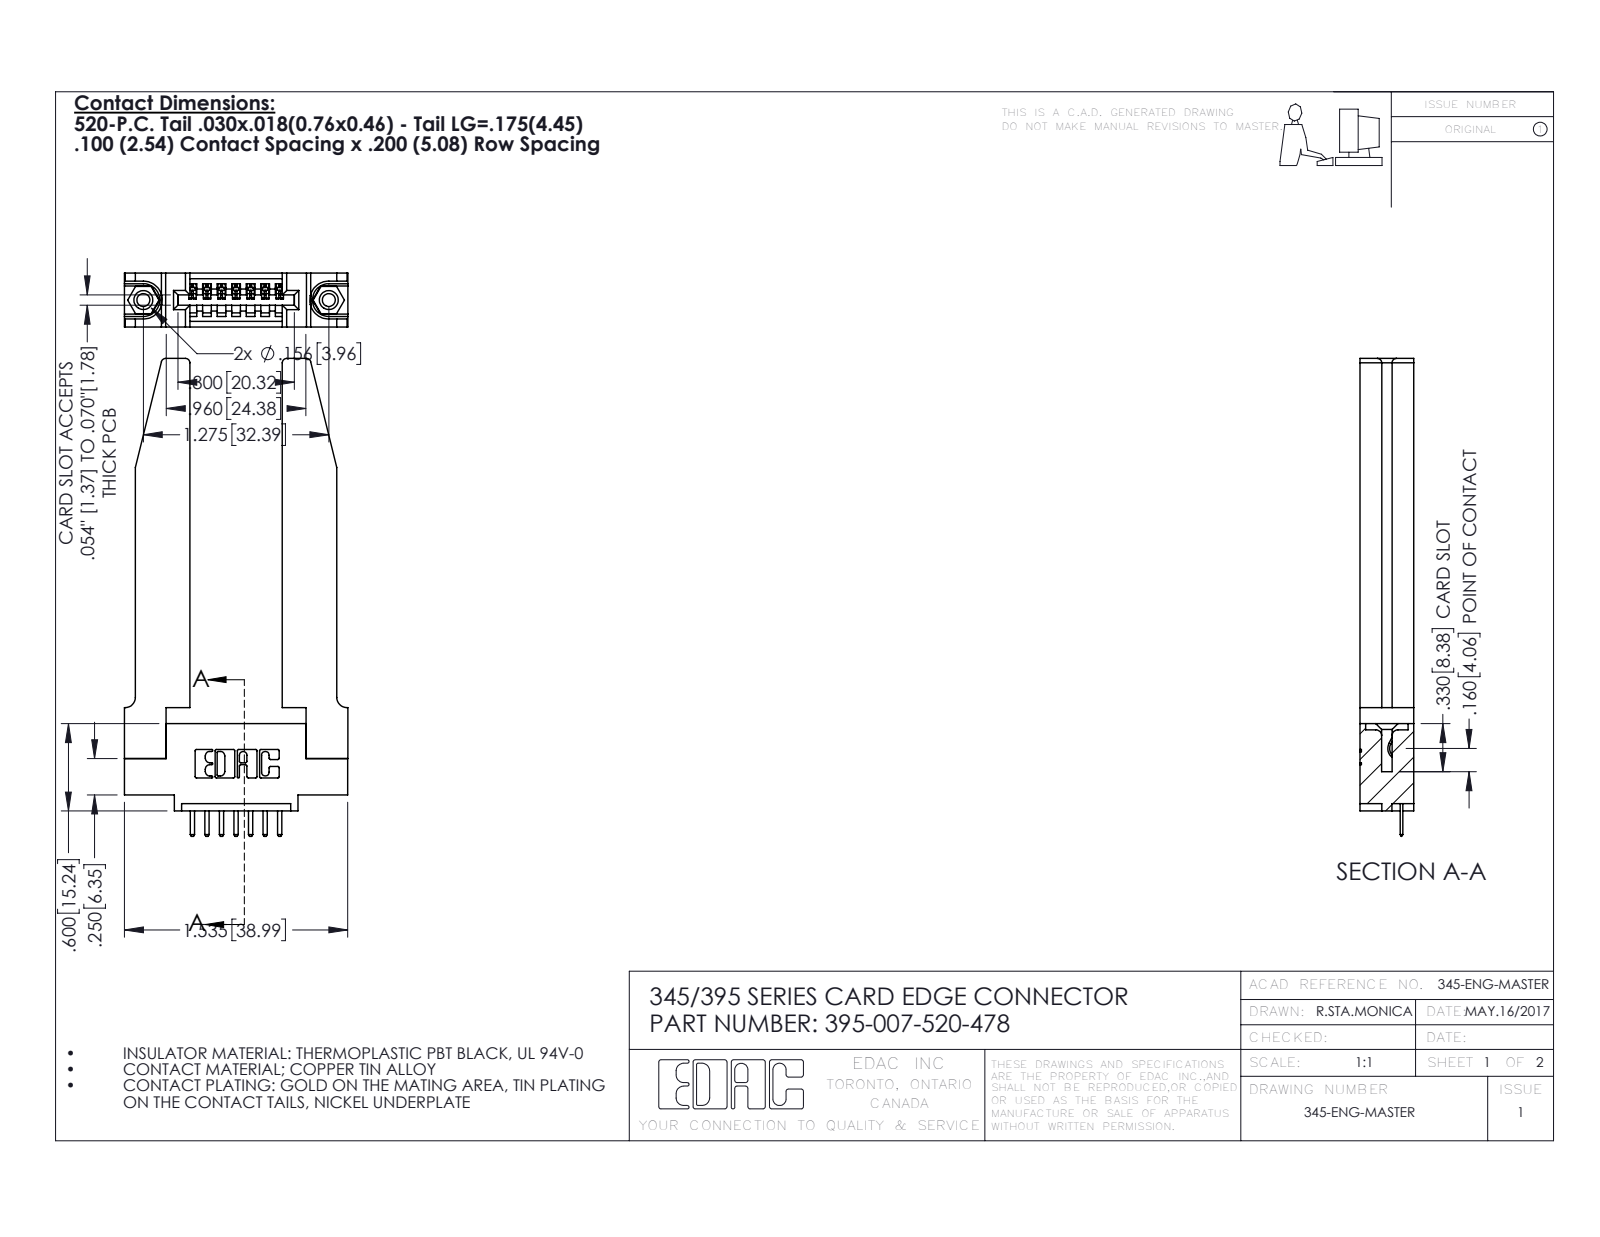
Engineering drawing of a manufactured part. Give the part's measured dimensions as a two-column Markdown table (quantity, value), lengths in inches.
| quantity | value |
| --- | --- |
| part name | 345 Part_0.110 Offset - 0.156 Dia-TH; 345-292-001_345-293-120; 395-007-520-478; 345-250-001_345-250-001-102 (+1 more) |
| STEP written by | SolidWorks 2016 (CONFIG_CONTROL_DESIGN) |
| units | inches |
| bodies | 12 solids, 798 faces (520 planar, 226 cylindrical, 52 other) |
| overall size | 3.285 × 1.536 × 0.37 |
| volume | 0.677 in³ |
| surface area | 16.75 in² |
| round holes (diameter × count) | 0.089 × 2, 0.125 × 2, 0.156 × 2, 0.064 × 1 |
| round bosses / shafts (diameter × count) | 0.155 × 2 |
| partial cylindrical surfaces (radius × count) | 0.01 × 22, 0.01 × 16, 0.006 × 14, 0.03 × 8, 0.007 × 6, 0.031 × 6, 0.026 × 3, 0.031 × 2 |
| main face-to-face distances | 0.37, 0.15, 0.22, 0.635, 0.072, 0.148, 0.298, 0.077, 0.071, 0.055 |
| hole center spacings | 0.27, 1.045, 1.275 |
